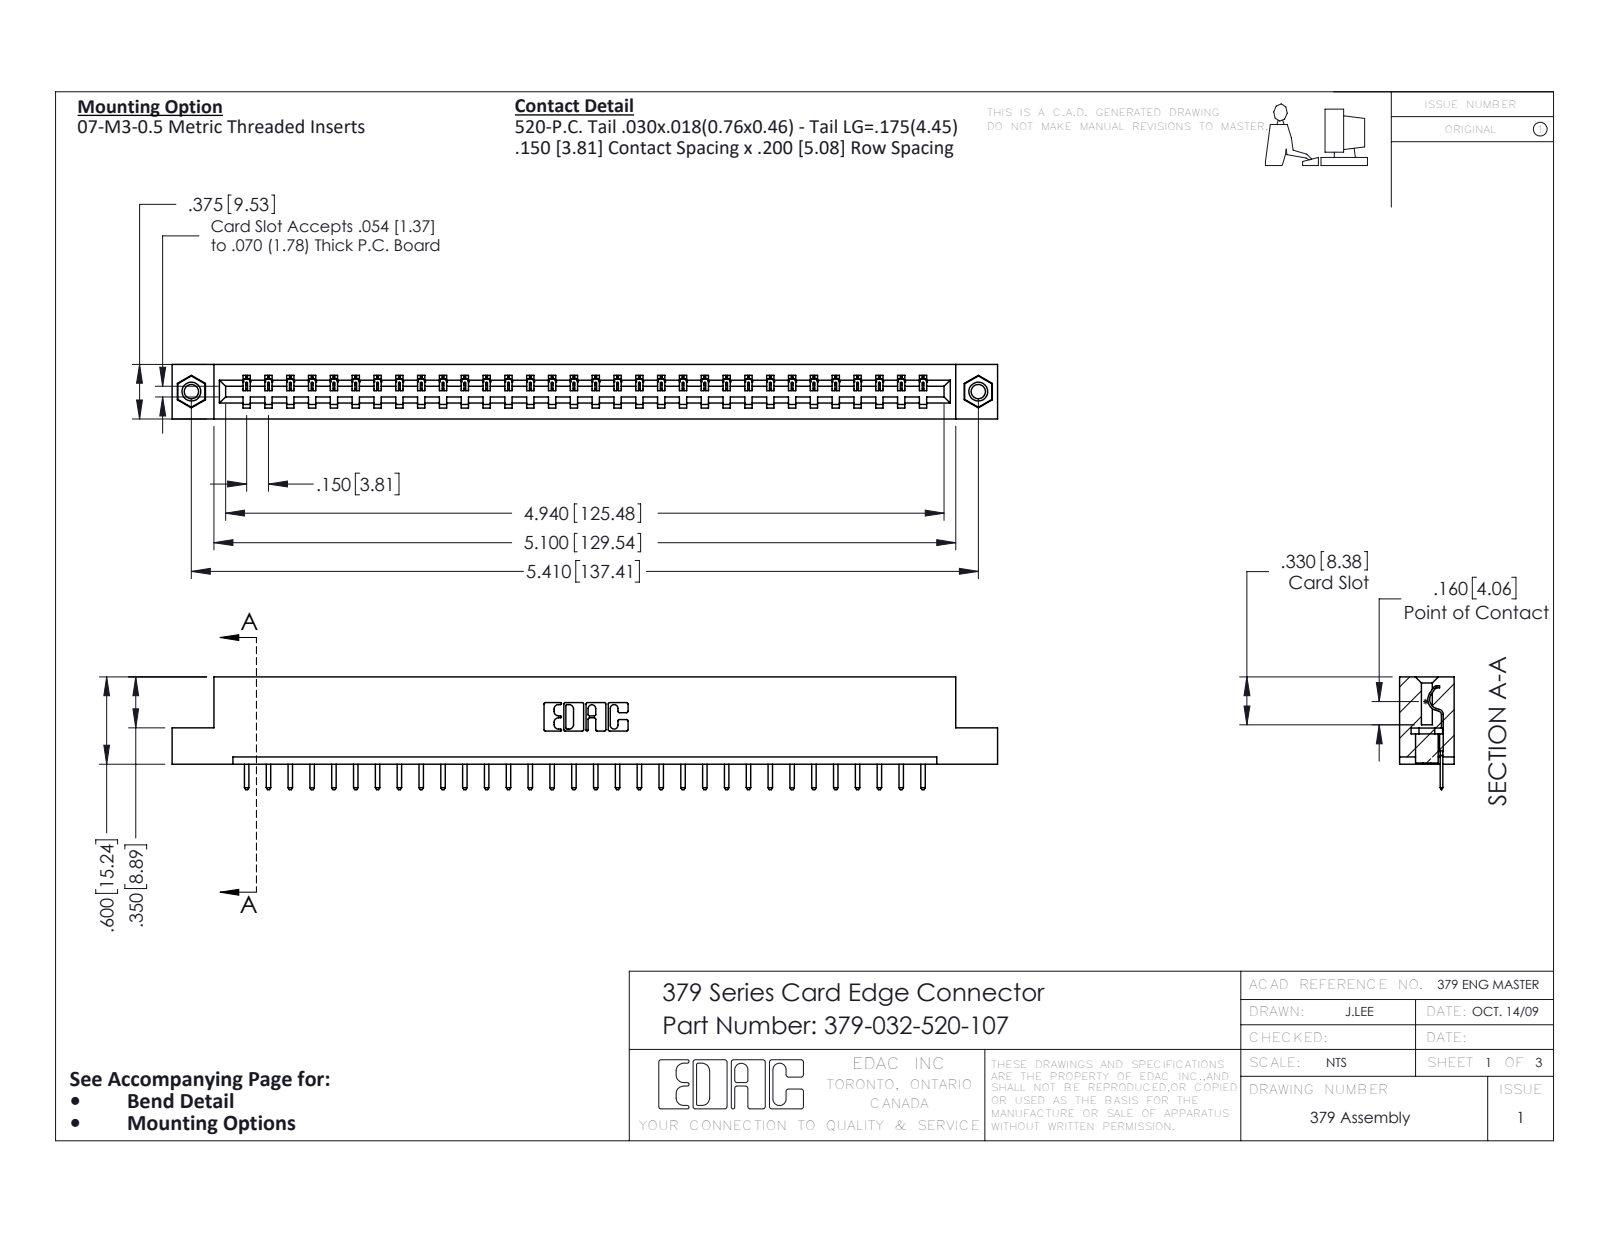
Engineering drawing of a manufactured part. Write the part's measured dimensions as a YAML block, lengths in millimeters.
part_name: "379 Part_Flush - .156 Dia - TI; 379-032-520-107; 345-292-001_345-293-120; 345-250-001_345-250-005-103"
step_written_by: "SolidWorks 2016 (CONFIG_CONTROL_DESIGN)"
units: millimeters
bodies: {solids: 35, faces: 2158, planar: 1510, cylindrical: 632, other: 16}
overall_size: [144.1, 19.7, 9.5]
volume: 14900
surface_area: 14920
round_holes:
  - {diameter: 2.5, count: 2}
  - {diameter: 3.2, count: 2}
  - {diameter: 4, count: 2}
round_bosses_or_shafts:
  - {diameter: 3.9, count: 2}
partial_cylinders:
  - {radius: 0.3, count: 66}
  - {radius: 0.2, count: 64}
  - {radius: 0.3, count: 22}
  - {radius: 0.2, count: 6}
  - {radius: 0.8, count: 6}
  - {radius: 0.7, count: 3}
  - {radius: 0.4, count: 1}
  - {radius: 0.6, count: 1}
face_to_face_distances: [7.6, 1.9, 9.5, 5.7, 15.2, 14, 5.1, 3.8, 3.8, 3.8]
hole_center_spacings: [137.4]
